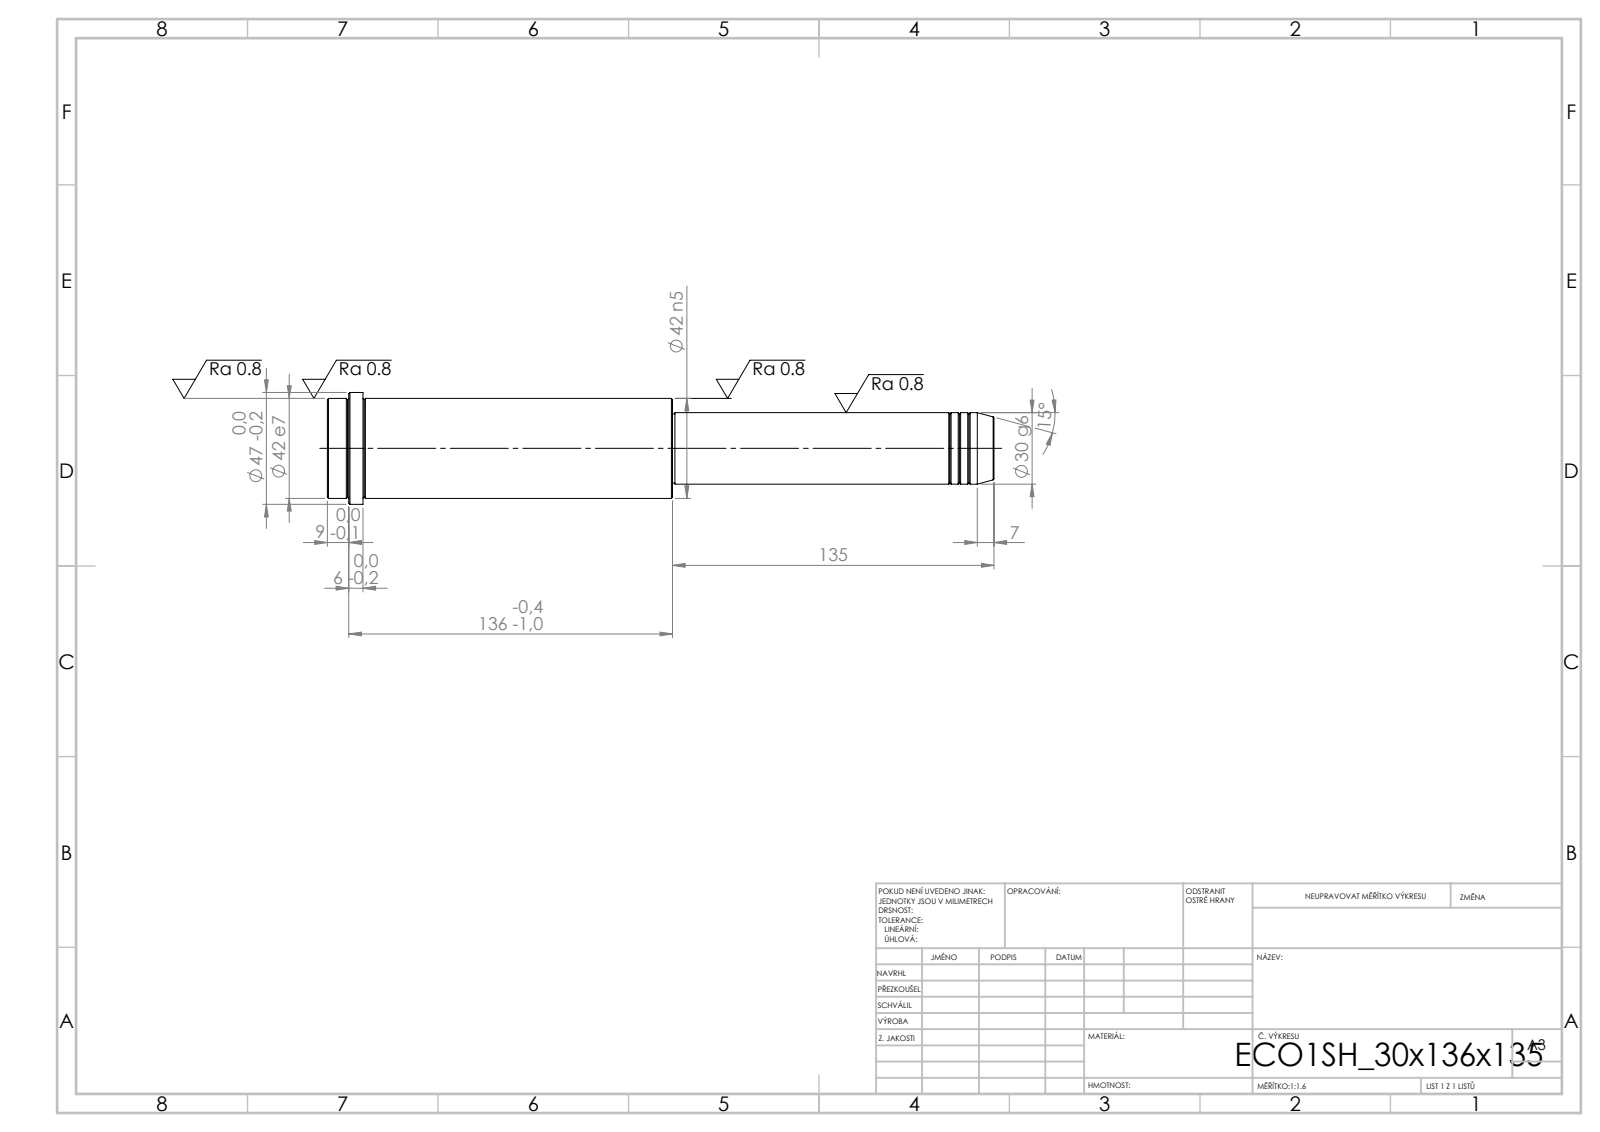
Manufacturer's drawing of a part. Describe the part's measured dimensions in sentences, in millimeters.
Its 3-D file was written by "SolidWorks 2019 (CONFIG_CONTROL_DESIGN)". It is 1 solid with 52 faces: 6 planar, 16 cylindrical and 30 other. Overall it measures 280 by 47 by 47 millimeters. Its volume is 297 507 cubic millimeters and its surface area 35 490 square millimeters. Round bosses or shafts: 1 of diameter 47, 1 of diameter 42, 1 of diameter 30, 1 of diameter 29. The main face-to-face distances are 145, 135, 280, 265, 130, 15, 271, 136, 6, 9.
